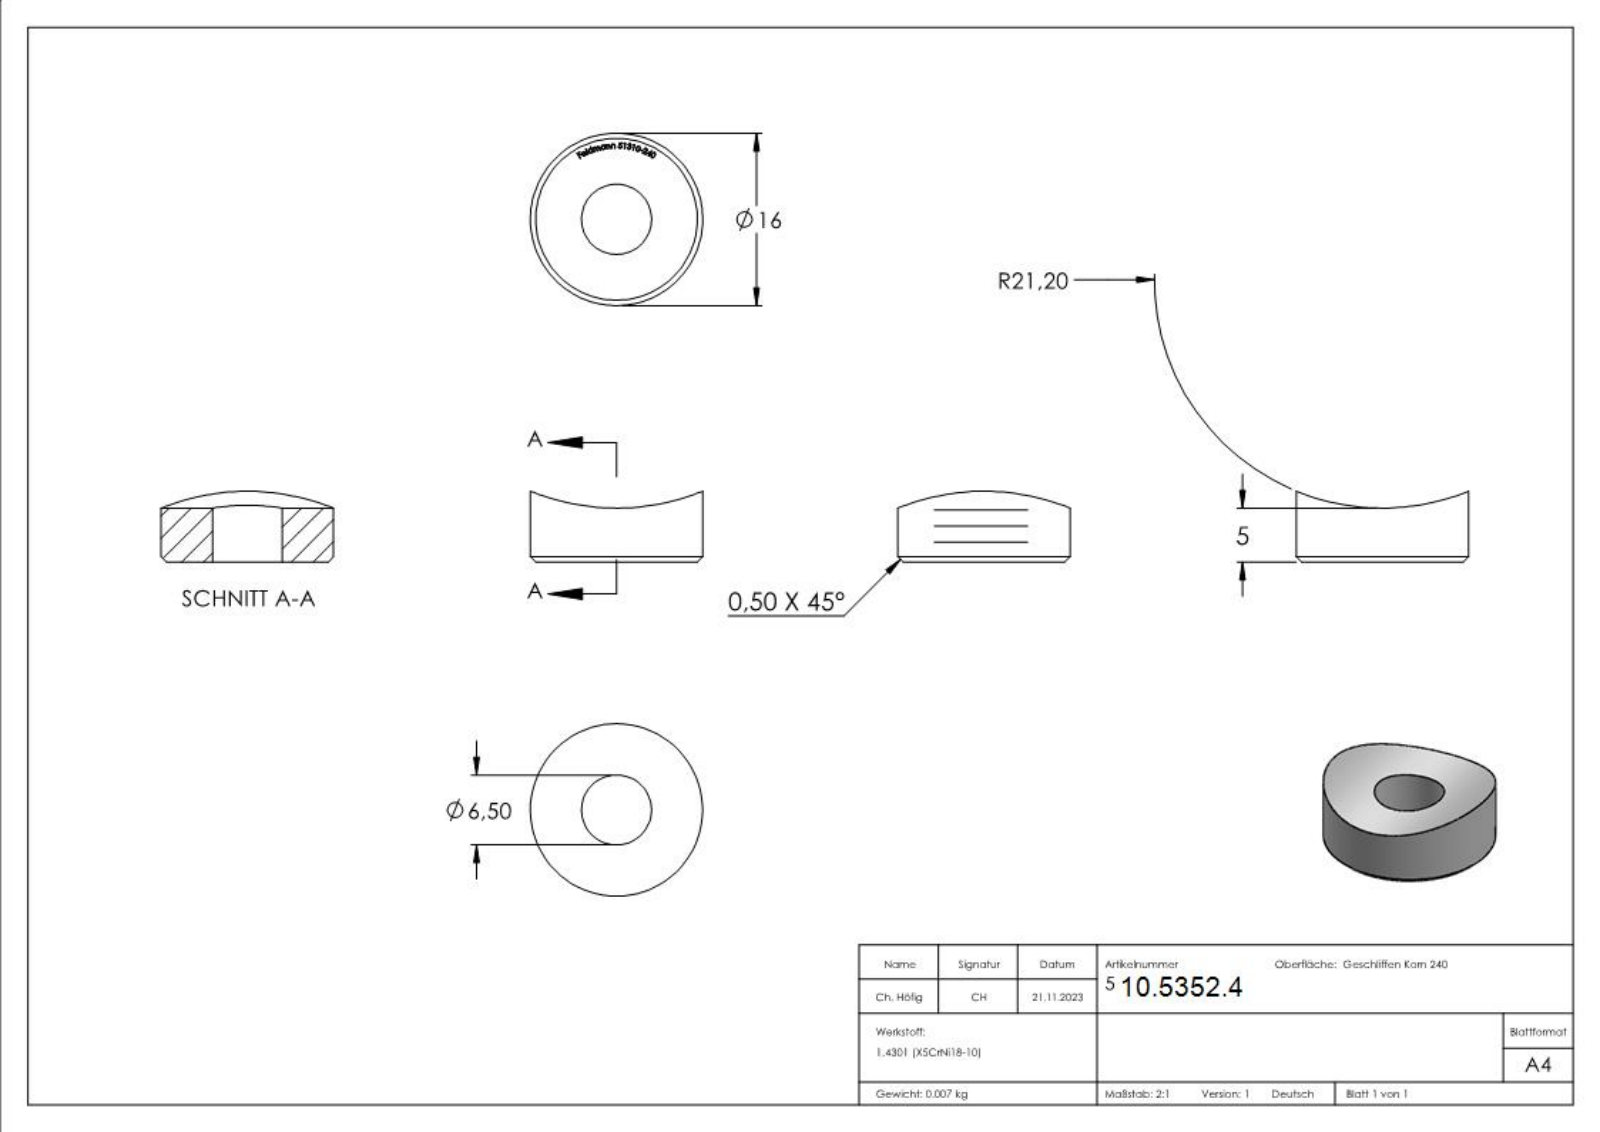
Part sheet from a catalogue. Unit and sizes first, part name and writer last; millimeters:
Units: millimetres
Overall size (bounding box): 16 × 16 × 6.57
Round holes (diameter × count): ⌀6.5 ×1
Round bosses / shafts (diameter × count): ⌀16 ×1
Partial cylindrical surfaces — rounded edges, fillets, slot ends (radius × count): R21.2 ×1
Main face-to-face distances: 0.53, 0.34, 0.48, 0.31, 0.58, 0.39, 0.54, 0.4, 0.47, 0.41
Volume: 908 mm³ · Surface area: 723 mm²
Bodies: 1 solid, 220 faces (122 planar, 3 cylindrical, 95 other)
Part name (STEP PRODUCT): 51310-240
STEP written by: SolidWorks 2018 (CONFIG_CONTROL_DESIGN)
